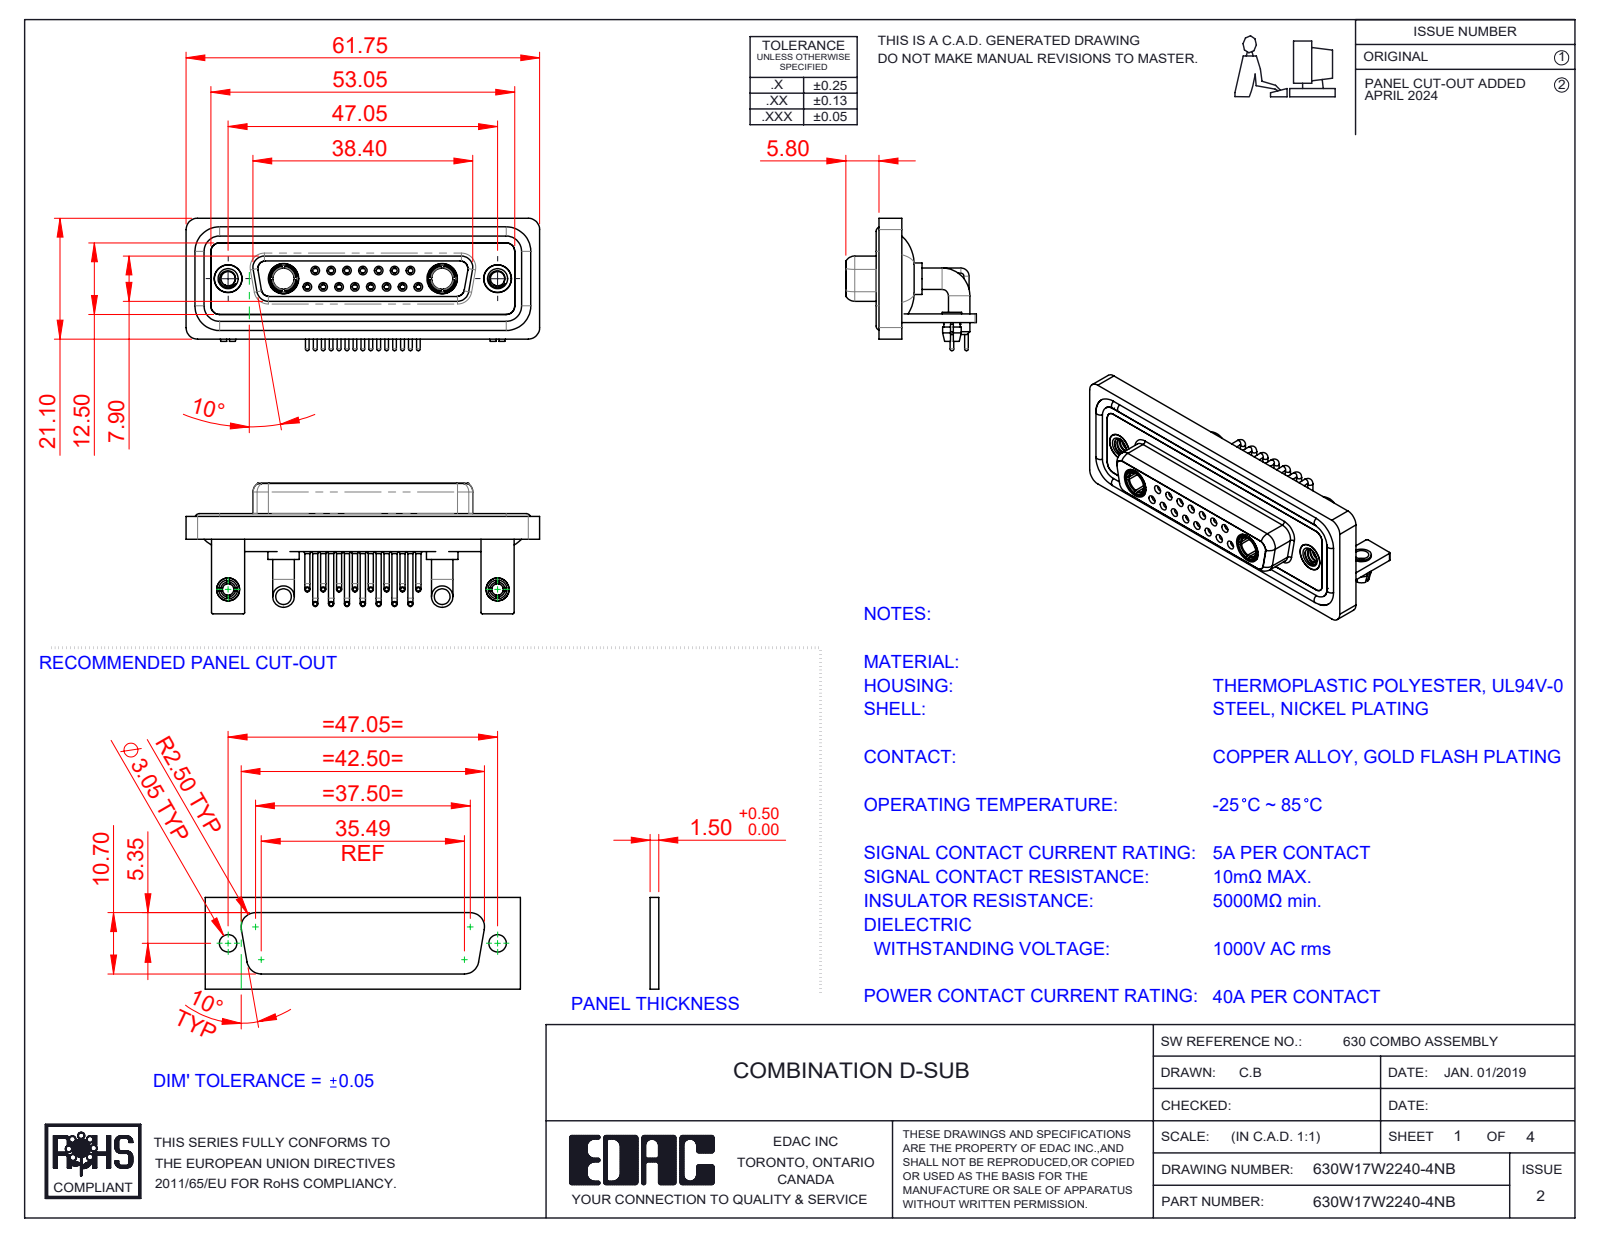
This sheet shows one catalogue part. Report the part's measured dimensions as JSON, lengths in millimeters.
{"part_name": "630Combo Waterproof Housing_25 Contacts; 630Combo Contact Row 1_50 Contacts; 630Combo Threaded Rivet_A; 630Combo Shell Front_25 Contacts (+7 more)", "step_written_by": "SolidWorks 2023 (CONFIG_CONTROL_DESIGN)", "units": "millimeters", "bodies": {"solids": 30, "faces": 1471, "planar": 456, "cylindrical": 637, "other": 378}, "overall_size": [61.75, 23.12, 22.8], "volume_mm3": 9028, "surface_area_mm2": 15567, "round_holes": [[2, 17], [0.9, 15], [1.1, 15], [1.5, 15], [1.6, 8], [1.7, 7], [2.5, 4], [4.85, 4], [3.2, 2], [3.7, 2], [4, 2], [4.05, 2]], "round_bosses_or_shafts": [[0.9, 15], [0.65, 15], [1.6, 11], [3.75, 4], [5.5, 2], [5.2, 2], [4.96, 2], [4.95, 2]], "partial_cylinders_radius": [[2, 19], [1.5, 18], [0.25, 16], [1.35, 8], [1.6, 8], [0.5, 5], [0.6, 4], [0.65, 4]], "face_to_face_distances": [0.4, 1.8, 2.9, 3.7, 1.5, 4.1, 1.1, 1.4, 1.6, 3.1], "hole_center_spacings": [3.16, 2.77, 5.54, 8.31, 5.04, 7.49, 11.08, 5.03]}
